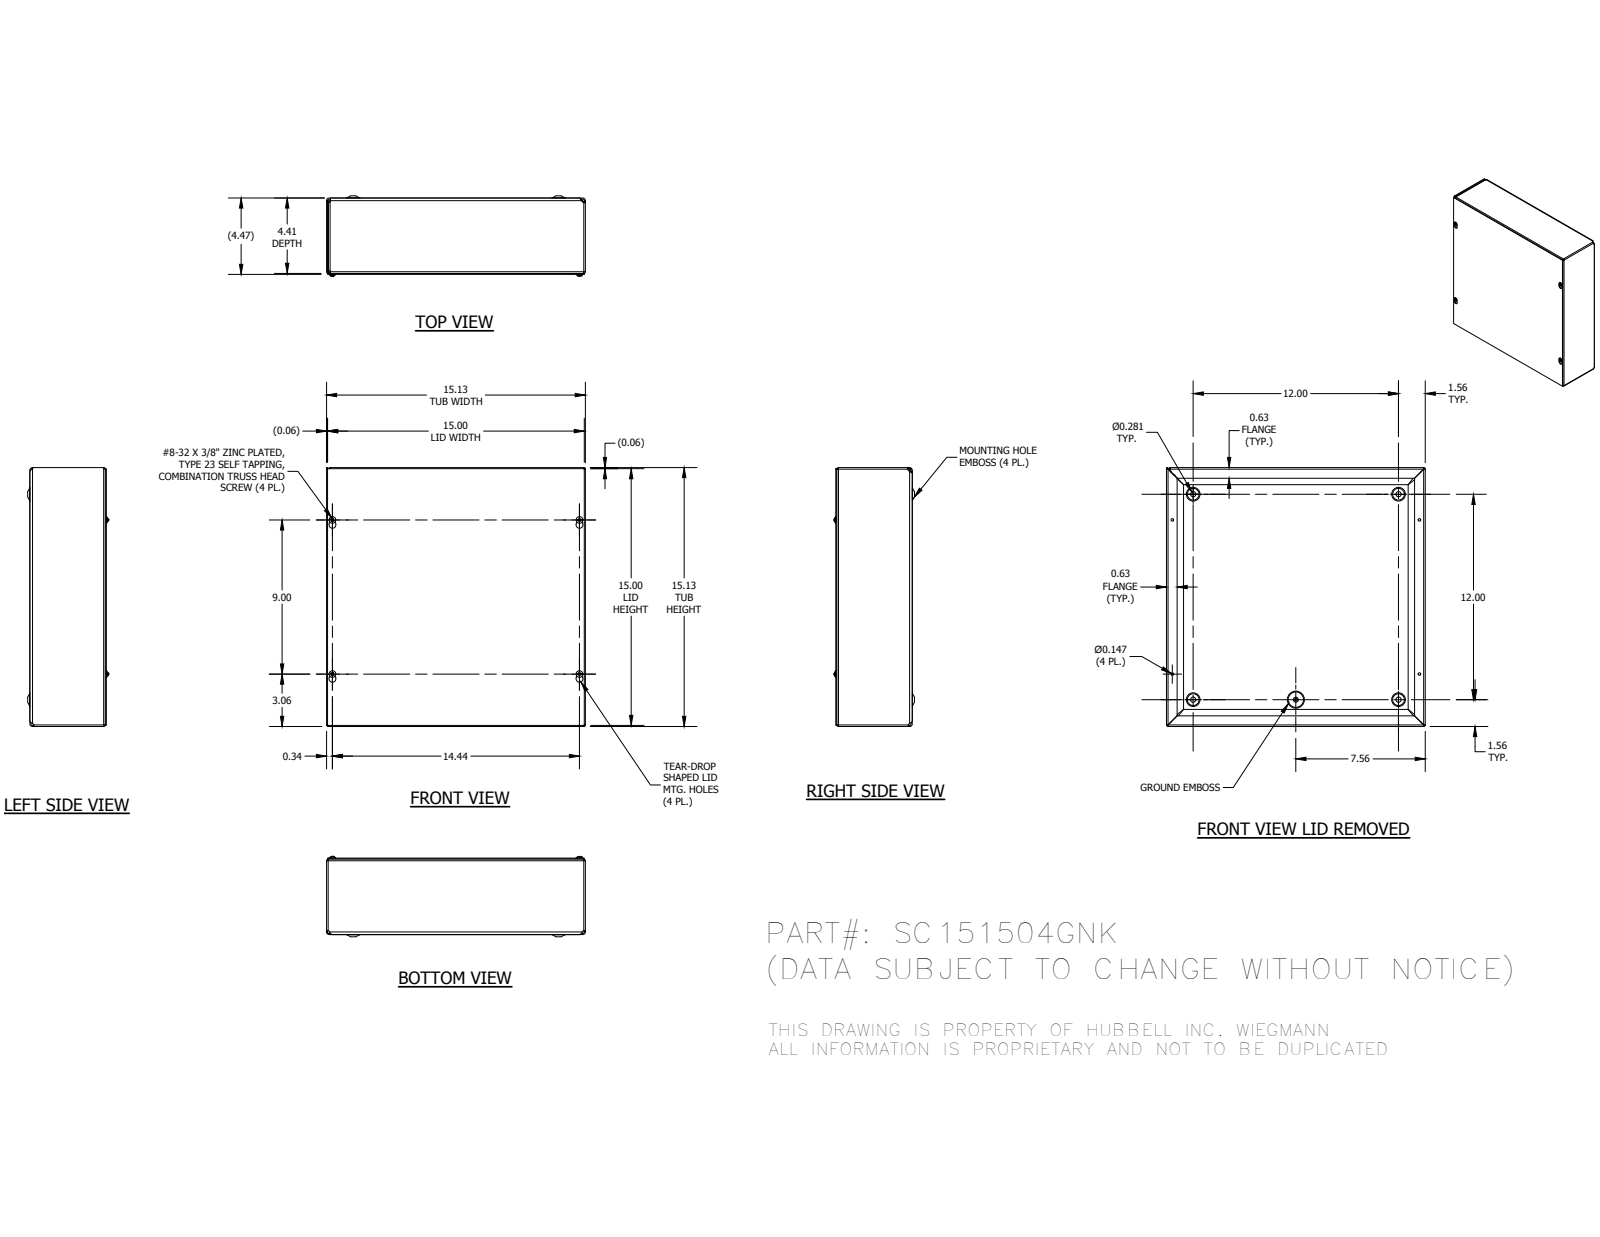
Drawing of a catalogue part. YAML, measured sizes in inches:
part_name: "SC1515GNKBKP; SC151504GNKWRA; SC1515GNKLID; 34056 (+1 more)"
step_written_by: "Autodesk Inventor 2014 (AUTOMOTIVE_DESIGN)"
units: inches
bodies: {solids: 7, faces: 358, planar: 133, cylindrical: 73, other: 152}
overall_size: [15.125, 15.125, 4.693]
volume: 48.93
surface_area: 1592
round_holes:
  - {diameter: 0.147, count: 4}
  - {diameter: 0.3, count: 4}
  - {diameter: 0.165, count: 1}
round_bosses_or_shafts:
  - {diameter: 0.384, count: 4}
  - {diameter: 0.164, count: 4}
  - {diameter: 0.228, count: 1}
partial_cylinders:
  - {radius: 0.031, count: 8}
  - {radius: 0.093, count: 8}
  - {radius: 0.055, count: 4}
  - {radius: 0.062, count: 4}
  - {radius: 0.094, count: 4}
  - {radius: 0.117, count: 4}
  - {radius: 0.124, count: 4}
  - {radius: 0.125, count: 4}
face_to_face_distances: [0.062, 4.343, 4.405, 0.063, 4.406, 4.468, 0.062, 15.063, 15.001, 15.125]
hole_center_spacings: [12, 6, 9, 10.57, 10.571, 12.741, 13.304, 13.417]
